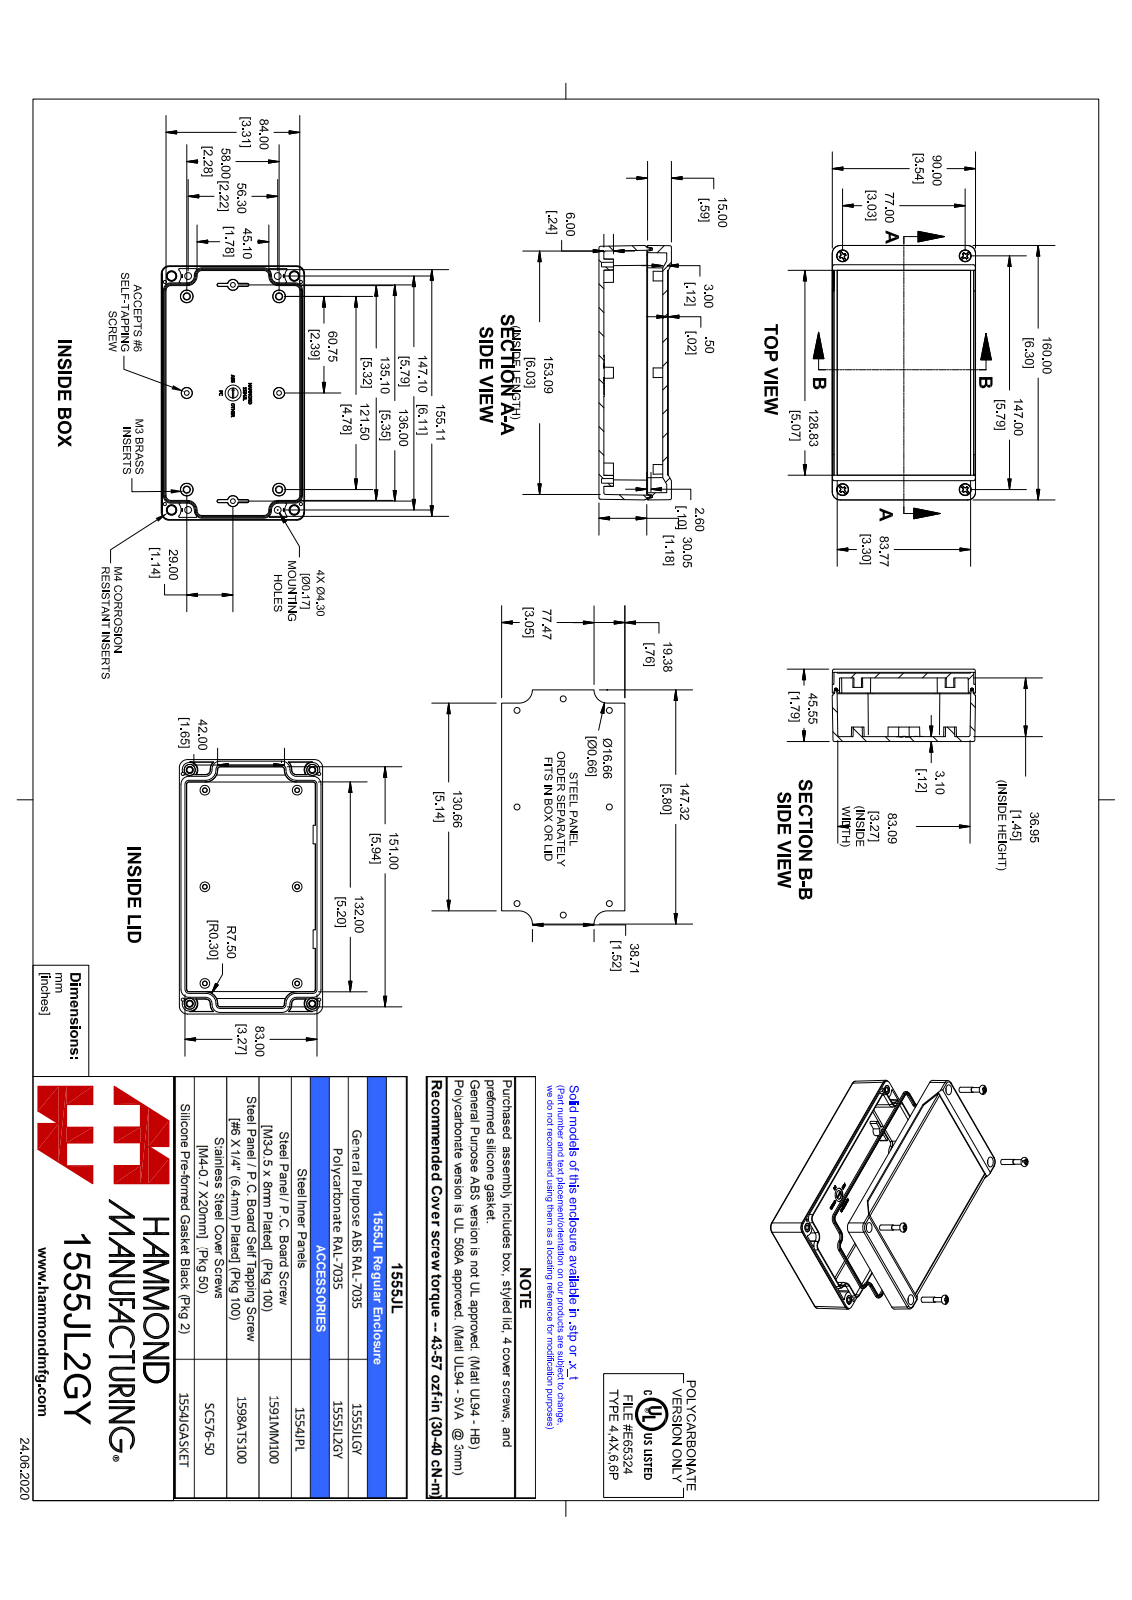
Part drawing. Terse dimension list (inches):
name: 1555JL2GY
written by: SolidWorks 2021 (AUTOMOTIVE_DESIGN)
unit: in
bodies: 15 solids, 1482 faces (400 planar, 323 cylindrical, 759 other)
size: 6.302 × 3.546 × 1.793
volume: 9.898 in³; area: 182.5 in²
holes: 4× ⌀0.079, 4× ⌀0.097, 4× ⌀0.128, 4× ⌀0.138, 4× ⌀0.181, 4× ⌀0.276
bosses: 4× ⌀0.25, 4× ⌀0.218, 4× ⌀0.21, 4× ⌀0.19, 4× ⌀0.154, 4× ⌀0.153, 4× ⌀0.15, 4× ⌀0.135
rounds: 18× R0.039, 16× R0.02, 8× R0.197, 4× R0.031, 4× R0.118, 4× R0.187
face distances: 0.118, 0.122, 1.695, 1.573, 1.577, 1.455, 0.12, 0.177, 0.138, 0.098
hole spacings: 0.196, 0.197, 0.626, 0.629, 0.678, 2.704, 2.707, 2.857
